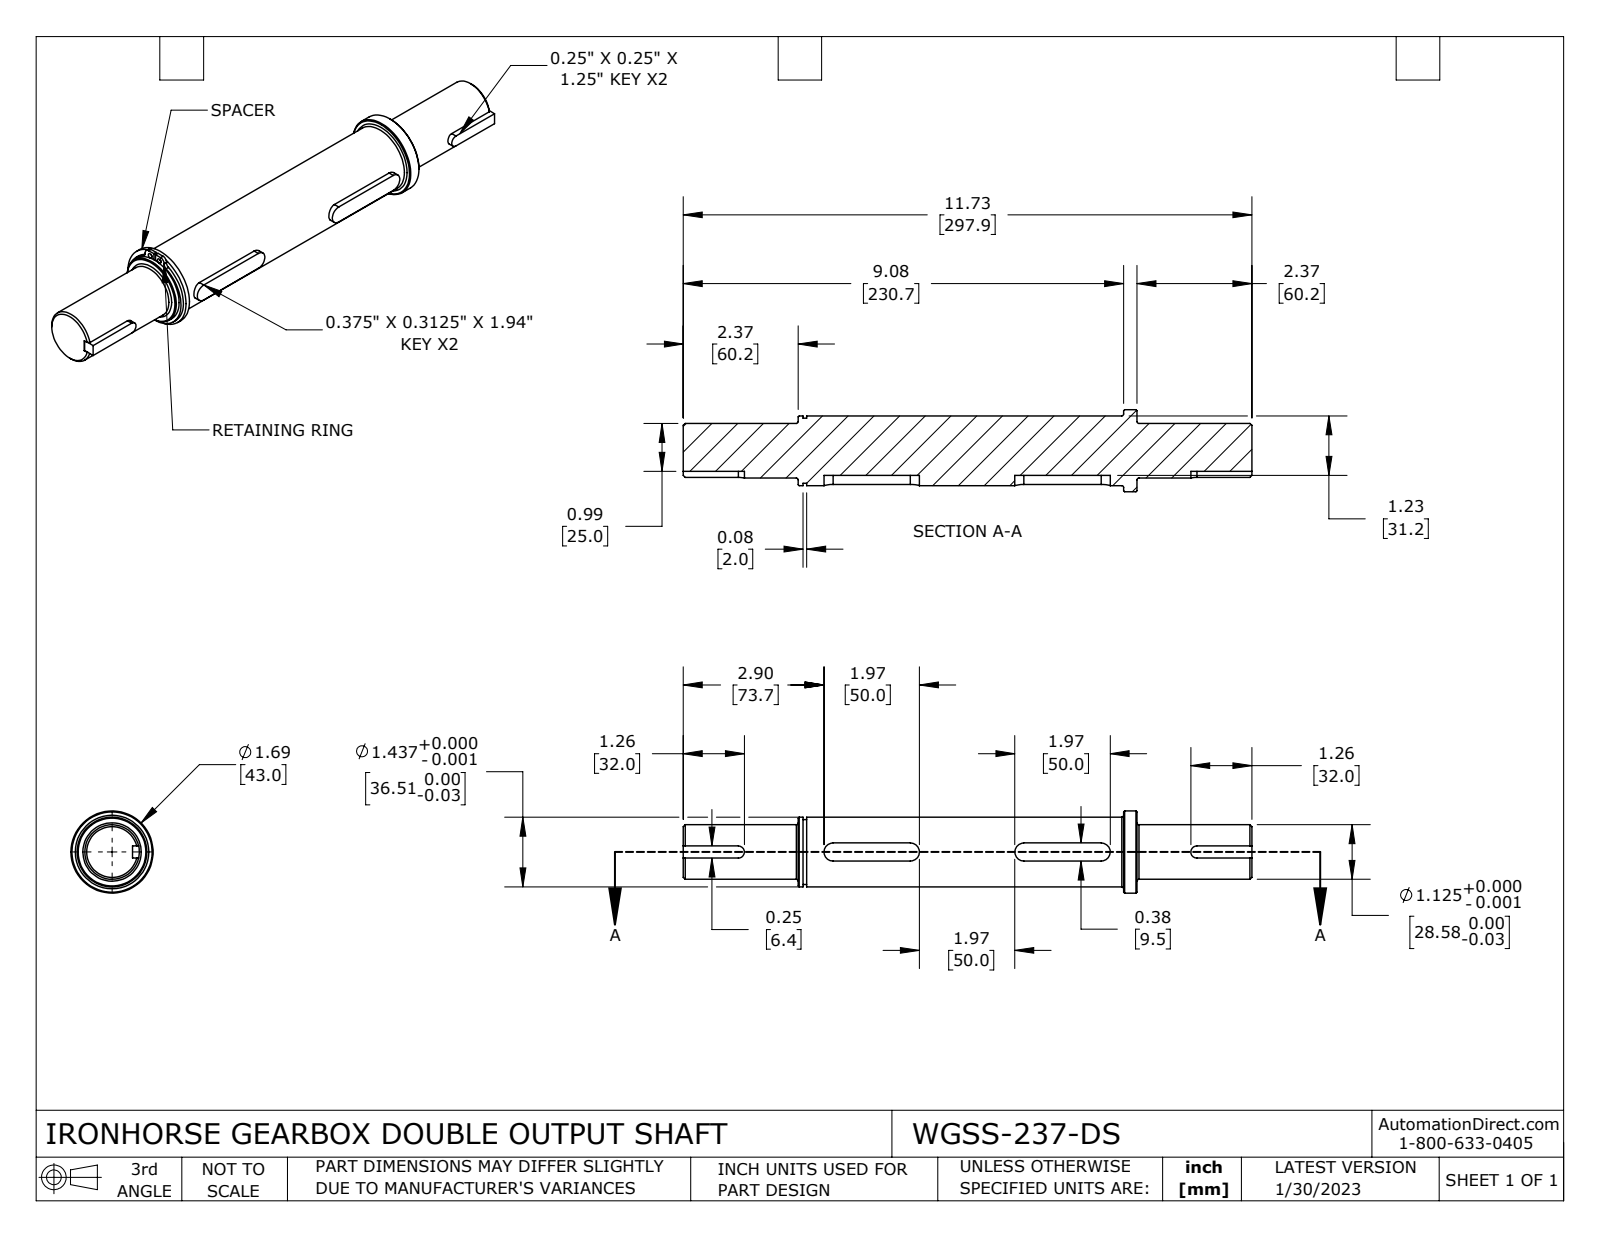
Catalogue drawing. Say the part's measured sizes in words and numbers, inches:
The part is named "WGSS-237-DS". Its 3-D file was written by "SolidWorks 2021 (CONFIG_CONTROL_DESIGN)". It is 7 solids with 112 faces: 47 planar, 49 cylindrical and 16 other. Overall it measures 11.728 by 1.707 by 1.693 inches. Its volume is 16.53 cubic inches and its surface area 67.43 square inches. Round holes: 2 of diameter 0.106, 1 of diameter 1.303, 1 of diameter 1.441. Round bosses or shafts: 1 of diameter 1.693, 1 of diameter 1.535, 1 of diameter 1.437, 1 of diameter 1.339, 1 of diameter 1.125. Partial cylindrical surfaces (rounded edges, fillets, slot ends): 4 of radius 0.1, 4 of radius 0.125, 4 of radius 0.188, 3 of radius 0.188, 1 of radius 0.187. The main face-to-face distances are 0.313, 0.063, 0.312, 9.358, 2.37, 0.085, 0.397, 0.063, 0.375, 6.811. The hole center spacings are 0.763, 0.264.
